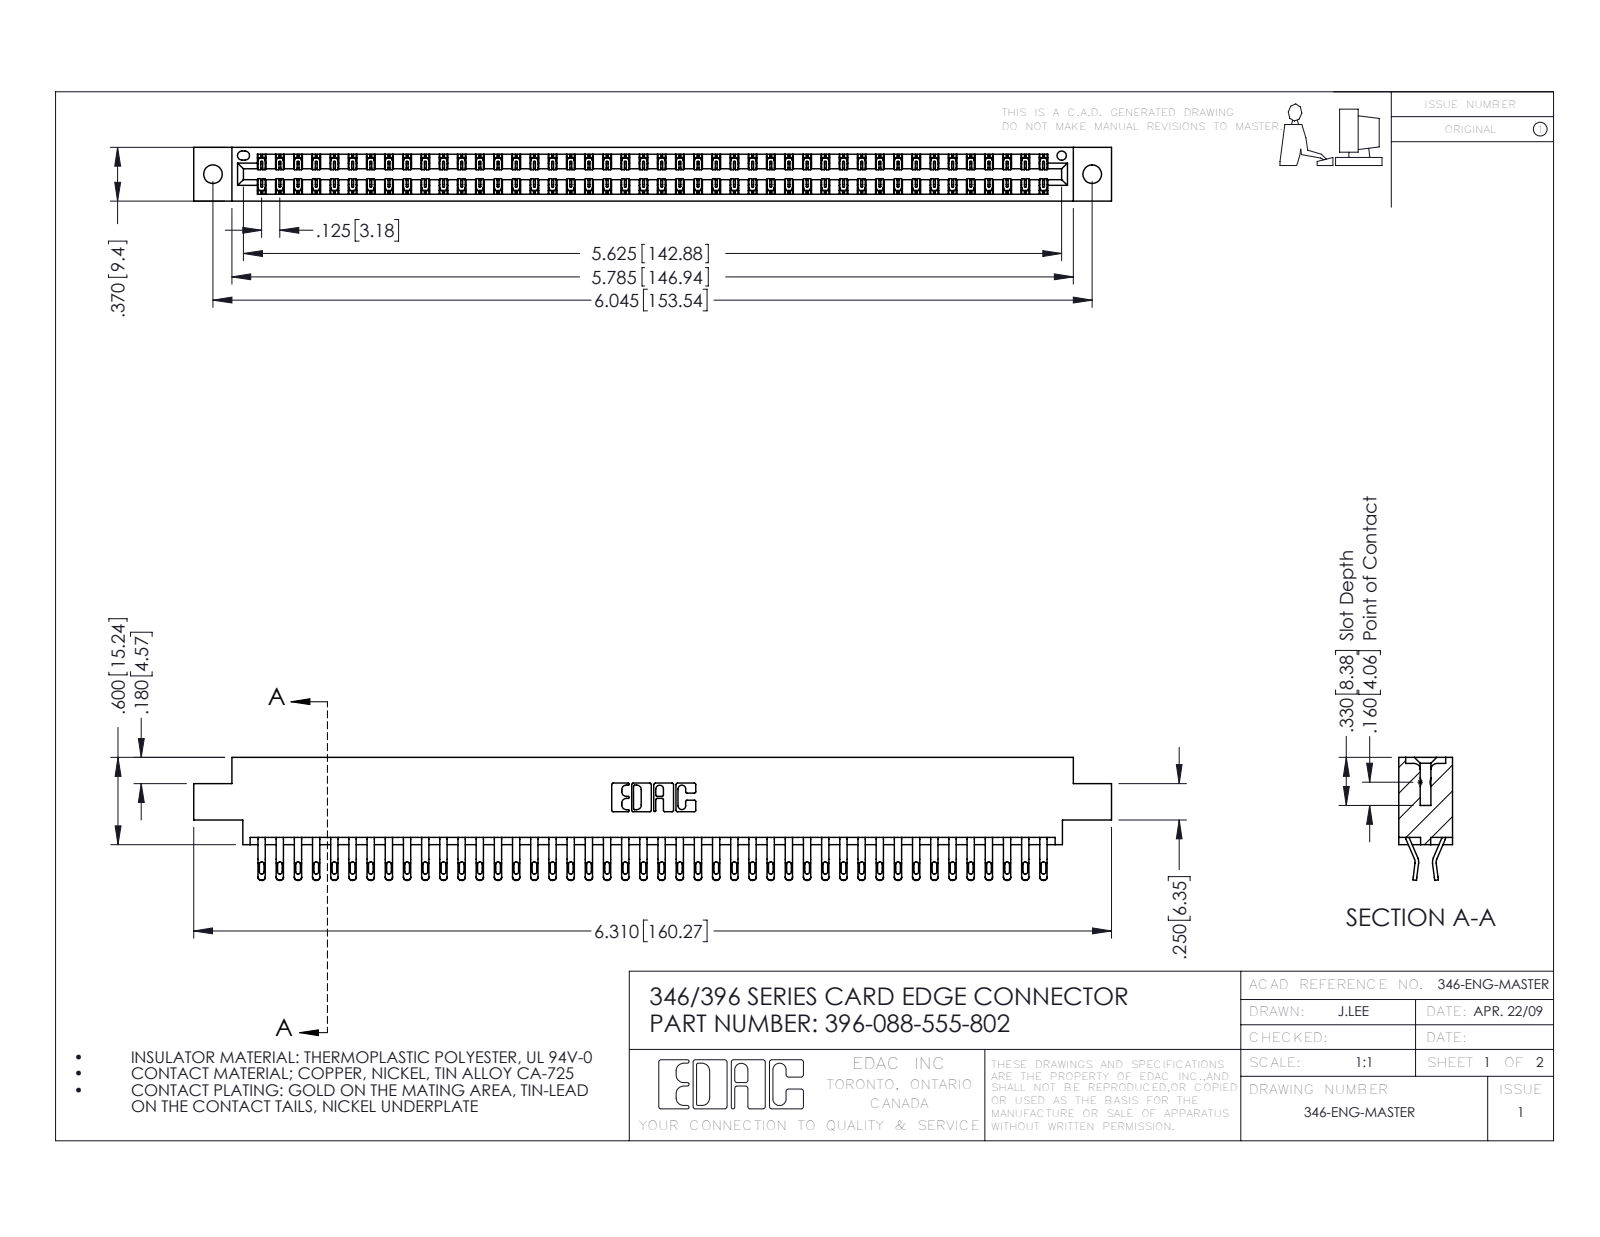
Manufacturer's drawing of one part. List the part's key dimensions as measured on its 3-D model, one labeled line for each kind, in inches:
Part name (STEP PRODUCT): 345-292-001_555 Tail; 346 Part_0.170 Offset - 0.128 Dia; 396-088-555-802
STEP written by: SolidWorks 2016 (CONFIG_CONTROL_DESIGN)
Units: inches
Bodies: 89 solids, 5230 faces (2984 planar, 2246 cylindrical, 0 other)
Overall size (bounding box): 6.31 × 0.845 × 0.37
Volume: 0.959 in³ · Surface area: 34.79 in²
Round holes (diameter × count): ⌀0.128 ×2, ⌀0.064 ×1
Partial cylindrical surfaces — rounded edges, fillets, slot ends (radius × count): R0.016 ×176, R0.02 ×176, R0.006 ×132, R0.01 ×22, R0.007 ×6, R0.031 ×6, R0.026 ×3, R0.01 ×2
Main face-to-face distances: 0.048, 0.322, 0.37, 0.25, 0.025, 0.072, 0.298, 0.275, 0.148, 0.222
Hole centre spacings: 0.246, 5.836, 6.045
